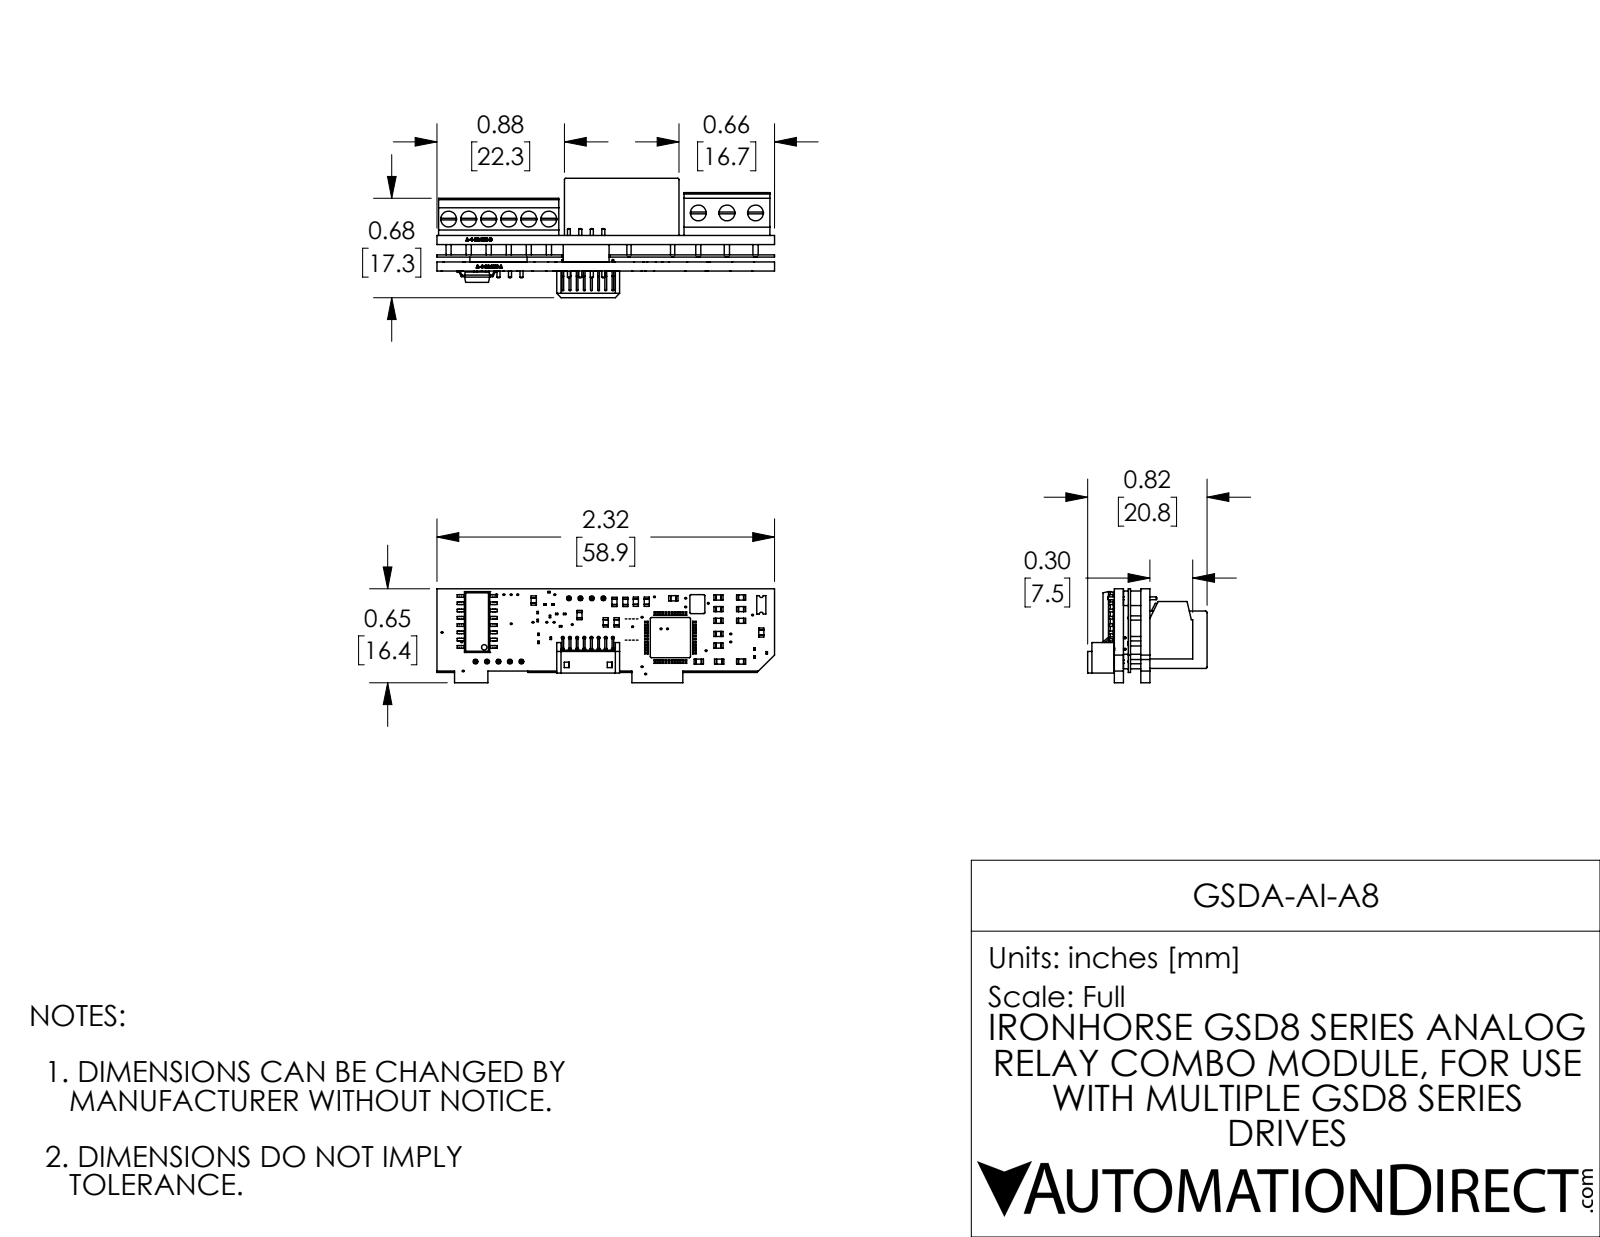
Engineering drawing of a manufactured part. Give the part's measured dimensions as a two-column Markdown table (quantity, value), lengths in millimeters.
| quantity | value |
| --- | --- |
| part name | GSDA-AI-A8 |
| STEP written by | SolidWorks 2017 (AUTOMOTIVE_DESIGN) |
| units | millimeters |
| bodies | 26 solids, 2138 faces (1480 planar, 455 cylindrical, 203 other) |
| overall size | 58.9 × 20.9 × 16.4 |
| volume | 6 980 mm³ |
| surface area | 9 755 mm² |
| round holes (diameter × count) | 0.3 × 30, 0.5 × 16, 0.8 × 9, 1.1 × 9, 2 × 9, 2.7 × 9, 1.2 × 3, 0.8 × 2, 0.9 × 1, 1.7 × 1 |
| round bosses / shafts (diameter × count) | 0.3 × 40, 0.9 × 9, 0.8 × 5 |
| partial cylindrical surfaces (radius × count) | 0.2 × 10, 0.1 × 8, 0.3 × 8, 0.1 × 4, 0.1 × 2, 0.3 × 2 |
| main face-to-face distances | 4.6, 1.6, 6.2, 3, 2.4, 2.8, 0.4, 3.8, 2.2, 0.9 |
| hole center spacings | 3.5, 7, 2, 10.5, 4, 5, 14, 18.1 |
